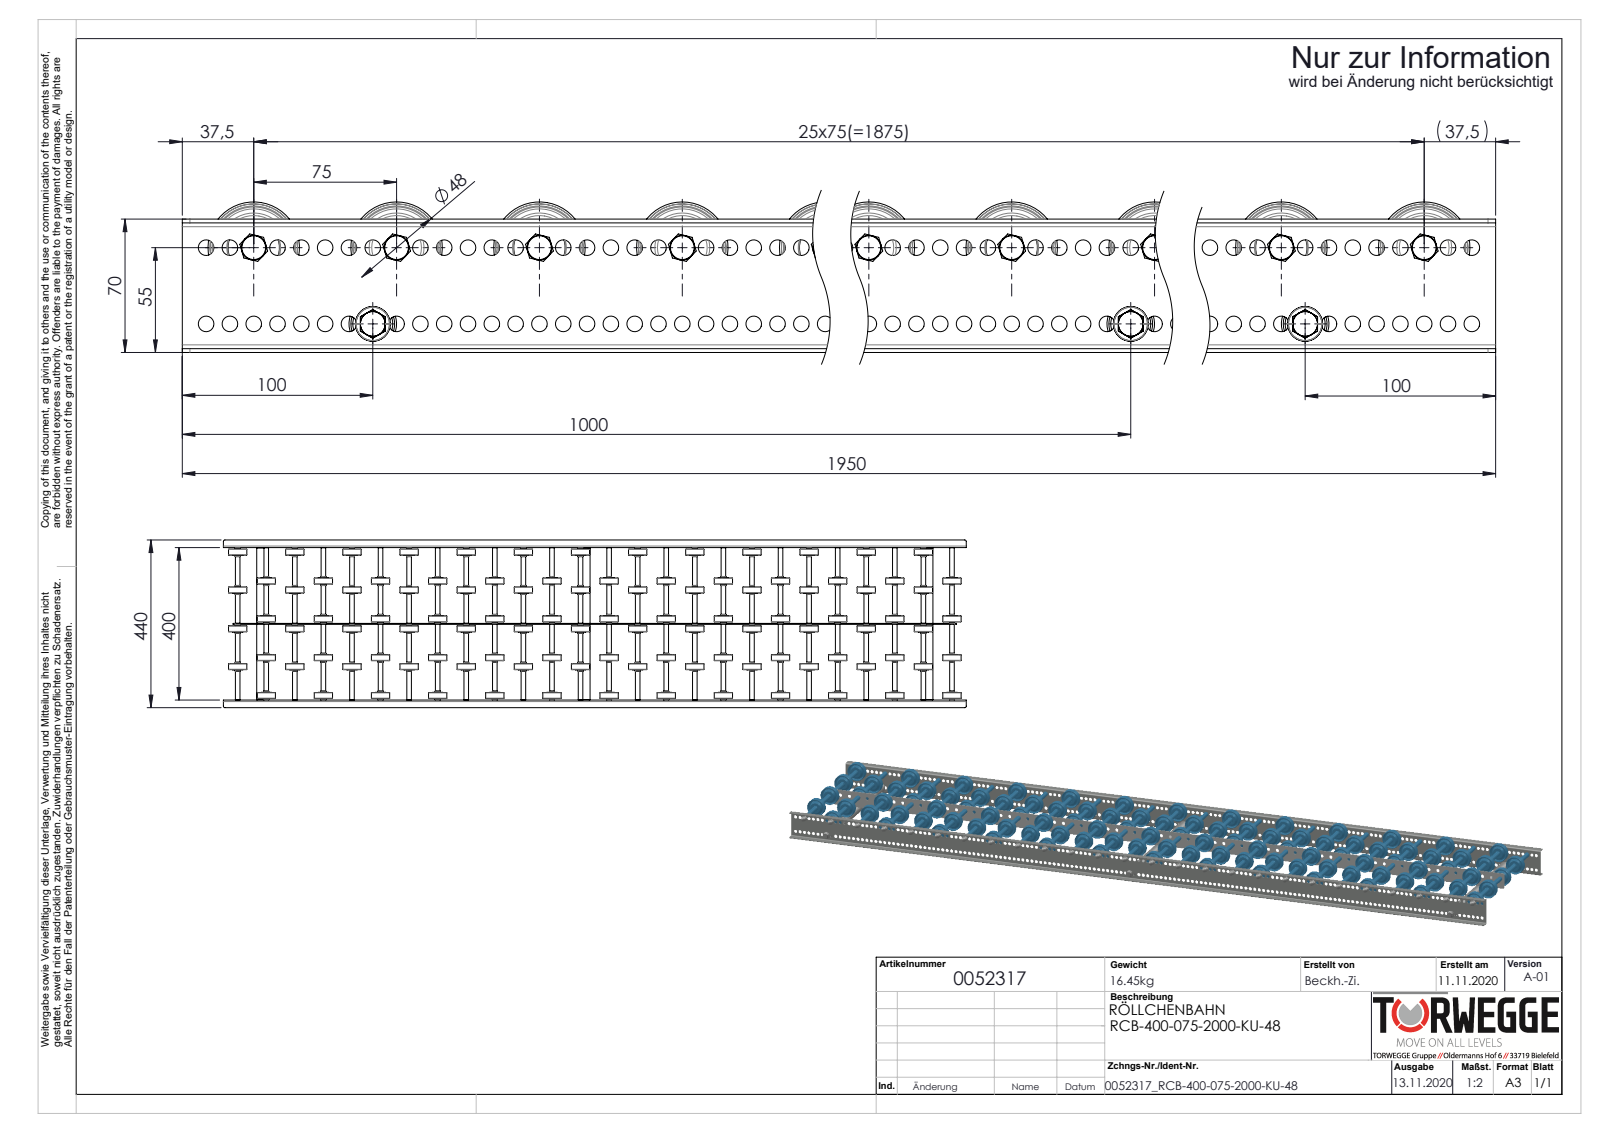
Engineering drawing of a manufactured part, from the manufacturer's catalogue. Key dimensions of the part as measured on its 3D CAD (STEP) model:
Part name (STEP PRODUCT): S100994_Sperrzahnschraube_M08x16-8.8-A2K; 0046278_KB-ROHR-12X1,75mm_KFG_L75,5; S106837_Gewindestange-M8-KFG_L420; S100100_Längstraverse-42x2,5_S100149_Lngstraverse-RB-L1899 (+6 more)
STEP written by: SolidWorks 2020 (AUTOMOTIVE_DESIGN)
Units: millimetres
Bodies: 304 solids, 11260 faces (1988 planar, 4020 cylindrical, 5252 other)
Overall size (bounding box): 1950 × 440 × 79
Volume: 4 041 000 mm³ · Surface area: 3 012 000 mm²
Round holes (diameter × count): ⌀8.2 ×310, ⌀8.5 ×76, ⌀6.65 ×26, ⌀9.65 ×26, ⌀13.7 ×26, ⌀6.8 ×3, ⌀21 ×3
Round bosses / shafts (diameter × count): ⌀8 ×29, ⌀48 ×26, ⌀27 ×26, ⌀12.7 ×26, ⌀12.5 ×26, ⌀12 ×26, ⌀25 ×3
Partial cylindrical surfaces — rounded edges, fillets, slot ends (radius × count): R4 ×8, R2 ×4, R5 ×4
Main face-to-face distances: 2, 402, 68, 404, 400, 201.1, 198.6, 200.9, 198.9, 203.1
Hole centre spacings: 12.5, 25, 37.5, 50, 62.5, 75, 87.5, 100
